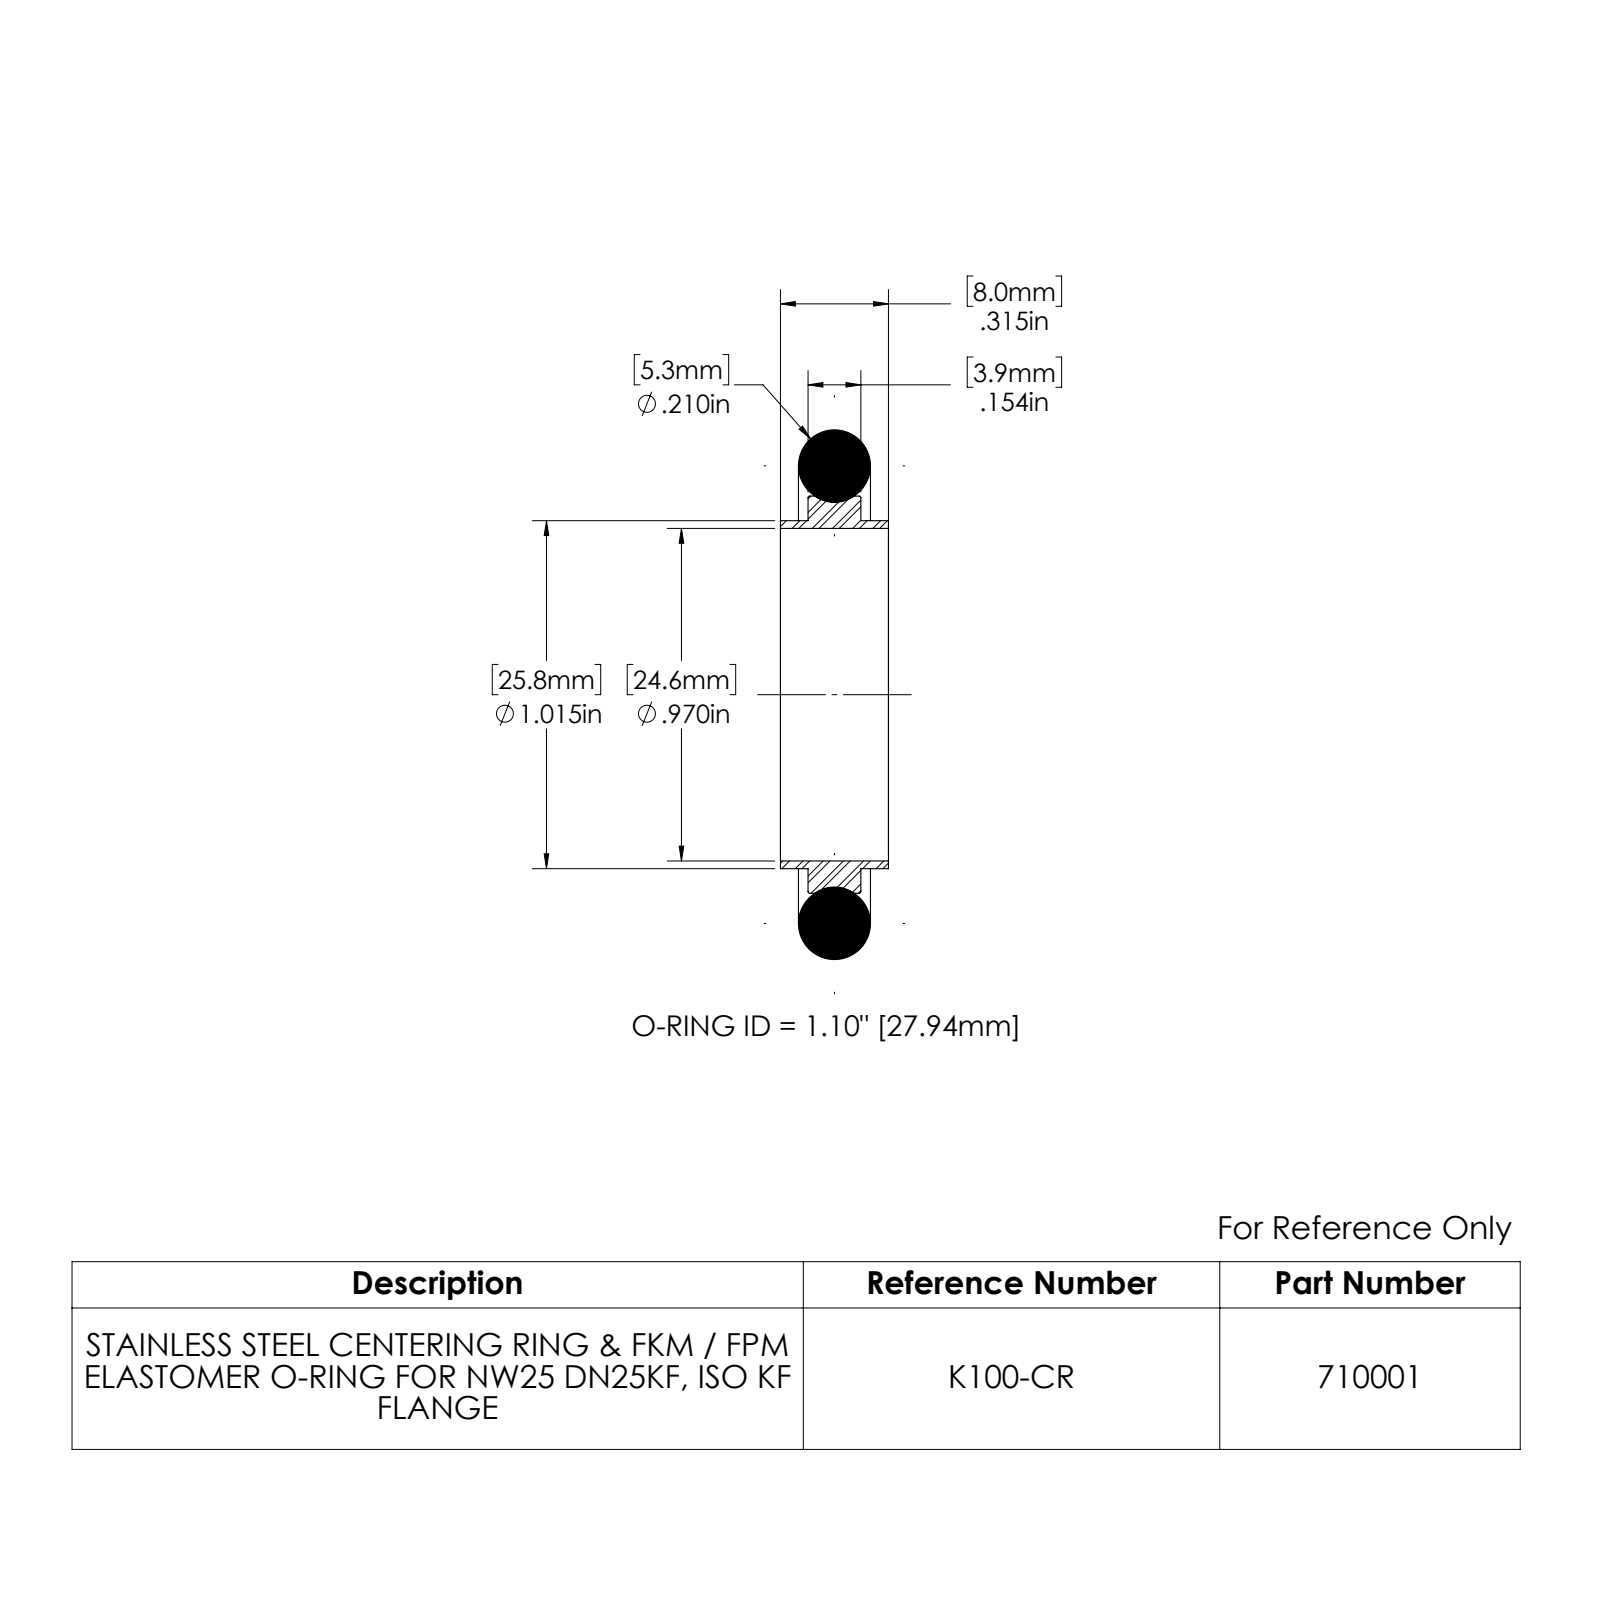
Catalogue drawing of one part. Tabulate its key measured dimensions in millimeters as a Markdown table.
| quantity | value |
| --- | --- |
| part name | 710001 |
| STEP written by | SolidWorks 2022 (AUTOMOTIVE_DESIGN) |
| units | millimeters |
| bodies | 2 solids, 22 faces (4 planar, 6 cylindrical, 12 other) |
| overall size | 38.8 × 38.8 × 8 |
| volume | 3 310 mm³ |
| surface area | 3 409 mm² |
| round holes (diameter × count) | 24.6 × 1 |
| round bosses / shafts (diameter × count) | 25.9 × 1 |
| main face-to-face distances | 2.1, 5.9, 3.8, 8 |
